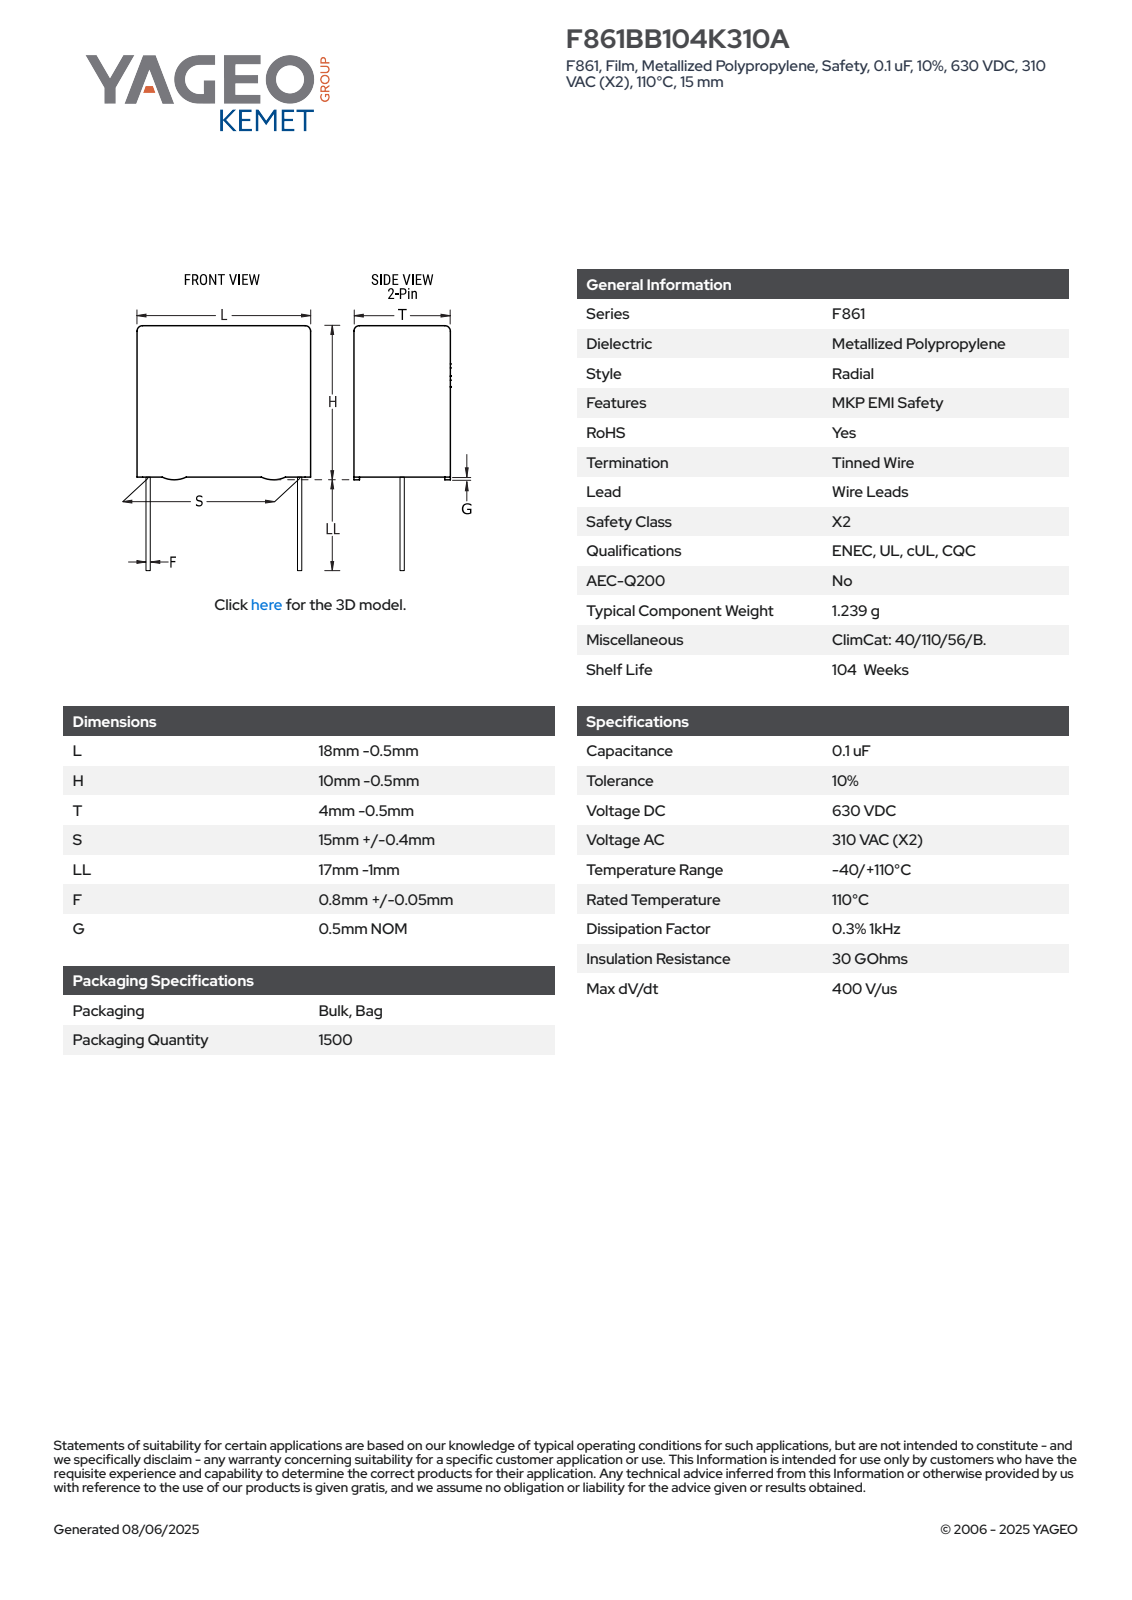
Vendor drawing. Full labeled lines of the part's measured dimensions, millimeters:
Part name (STEP PRODUCT): CFR_RBG_18X10X4_L17.5H9.5T3.5S15LL16F0.85G0.5
STEP written by: SolidWorks 2014 (AUTOMOTIVE_DESIGN)
Units: millimetres
Bodies: 4 solids, 89 faces (81 planar, 8 cylindrical, 0 other)
Overall size (bounding box): 25.5 × 17.5 × 3.5
Volume: 569 mm³ · Surface area: 625 mm²
Round bosses / shafts (diameter × count): ⌀0.85 ×2
Partial cylindrical surfaces — rounded edges, fillets, slot ends (radius × count): R0.5 ×4
Main face-to-face distances: 3.5, 9, 17.5, 3.3, 3.1, 0.5, 9.5, 16, 16.5, 25.5
